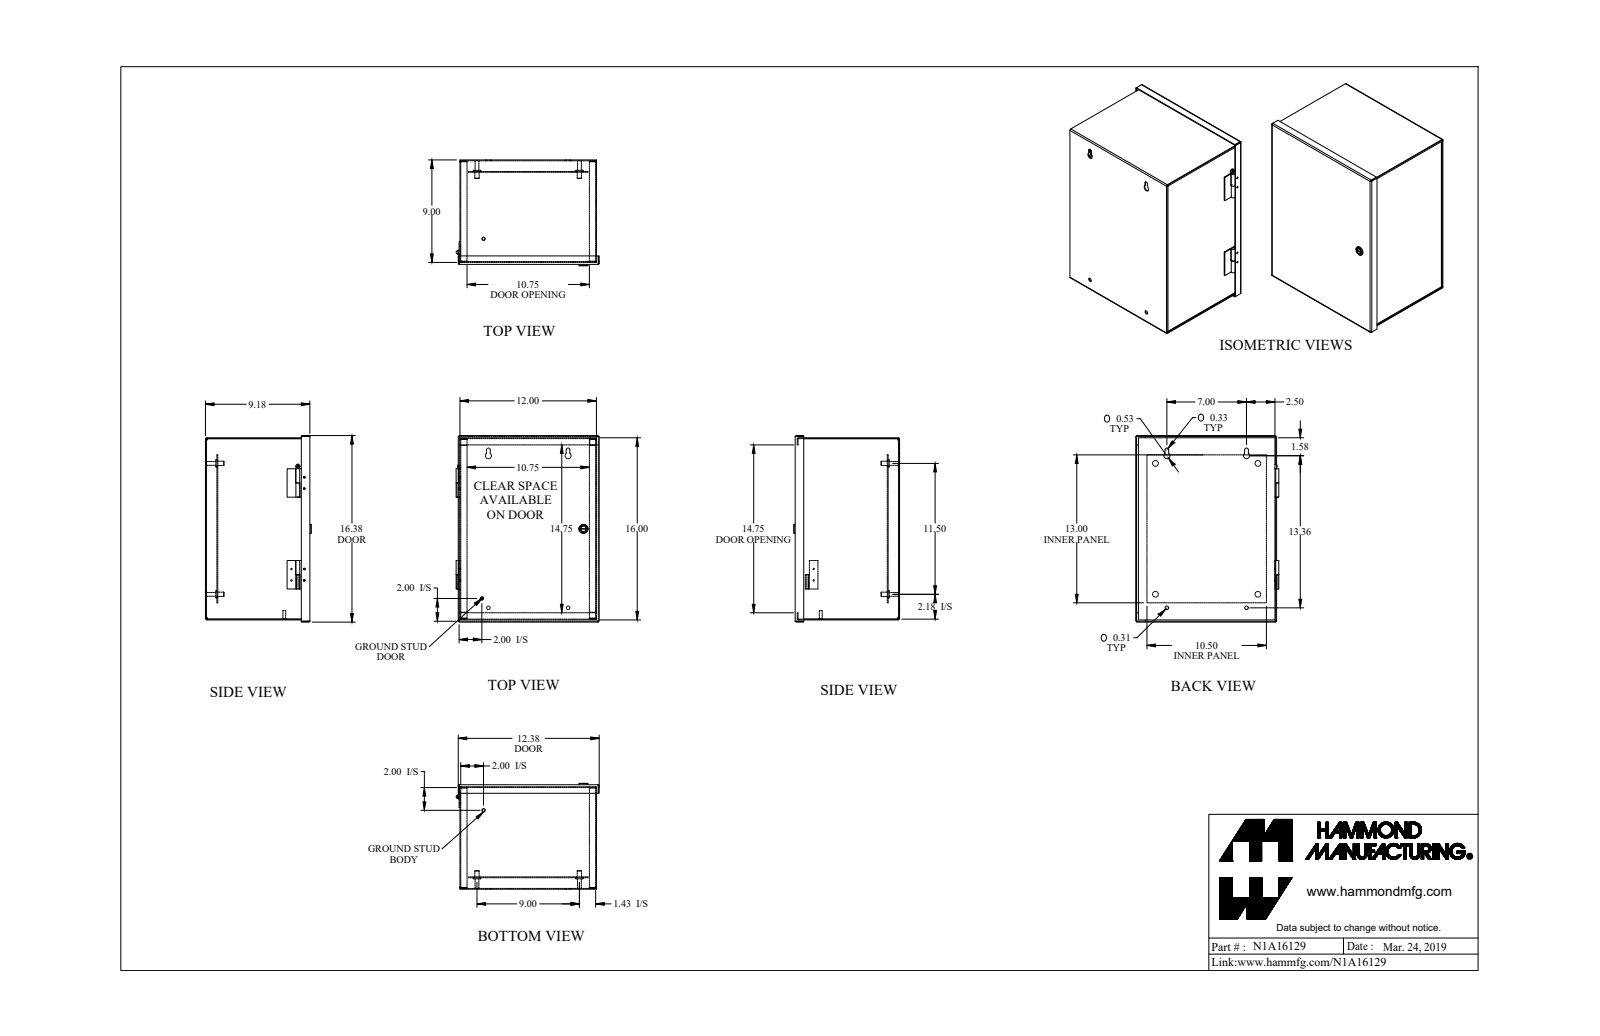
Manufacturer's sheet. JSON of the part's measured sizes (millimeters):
{"part_name": "N1A16129", "step_written_by": "SolidWorks 2018 (AUTOMOTIVE_DESIGN)", "units": "millimeters", "bodies": {"solids": 23, "faces": 520, "planar": 294, "cylindrical": 182, "other": 44}, "overall_size": [416.2, 319.4, 236.2], "volume_mm3": 1368000, "surface_area_mm2": 1500000, "round_holes": [[3.6, 8], [12.7, 4], [7.8, 2], [7.9, 2], [11.3, 2], [4.3, 1], [4.7, 1], [13.1, 1]], "round_bosses_or_shafts": [[3.3, 8], [9.5, 5], [16.5, 4], [8.4, 4], [25.4, 2], [7.1, 2], [6.4, 2], [20, 1]], "partial_cylinders_radius": [[0.9, 16], [2.7, 16], [1.5, 2], [3.9, 2], [4.2, 2], [6.8, 2], [0.8, 1], [3.2, 1]], "face_to_face_distances": [1.8, 231.3, 25.6, 205.6, 303, 404.6, 229.4, 233.1, 304.8, 27.5], "hole_center_spacings": [25.4, 28.4, 39.4, 51.6, 146.3, 204.8, 204.8, 205.4]}
